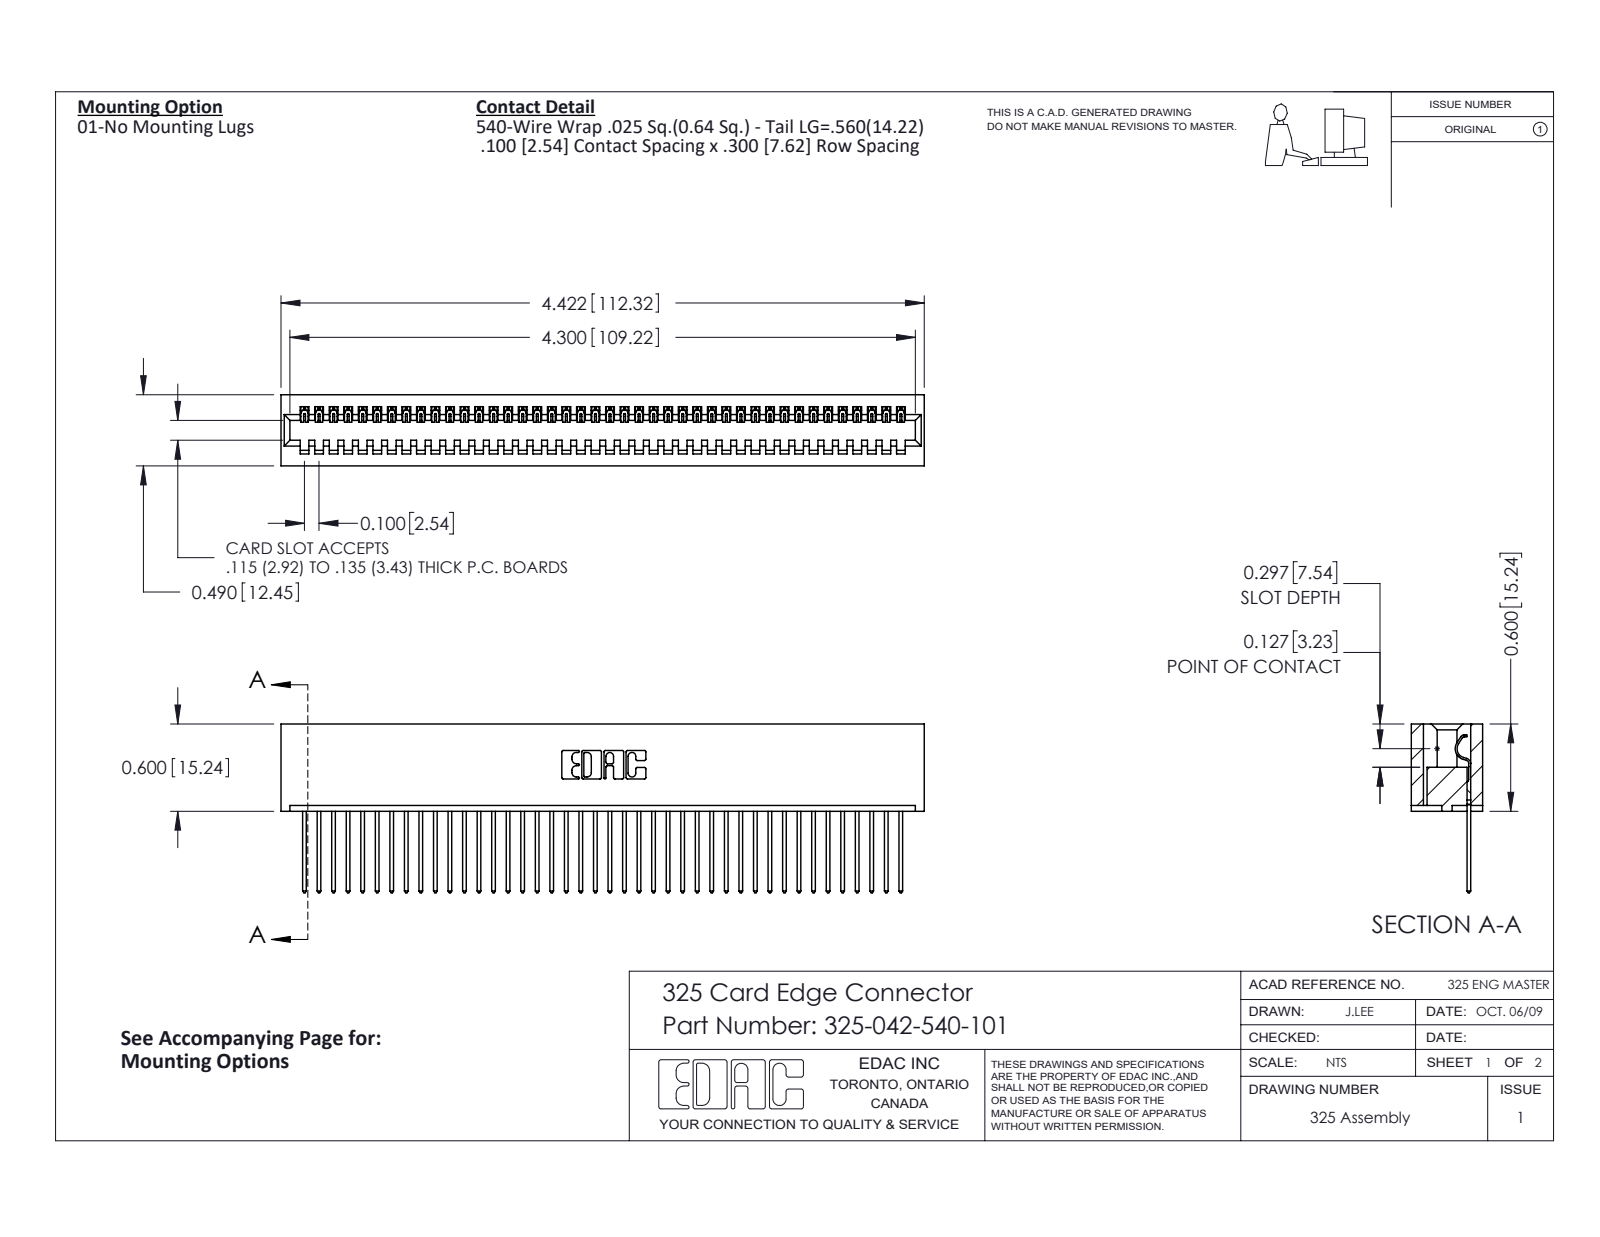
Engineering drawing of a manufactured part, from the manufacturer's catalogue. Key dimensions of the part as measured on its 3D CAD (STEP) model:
Part name (STEP PRODUCT): 325-042-540-101; 325-292-001_325-293-140; 325 Part_Lugless
STEP written by: SolidWorks 2016 (CONFIG_CONTROL_DESIGN)
Units: inches
Bodies: 43 solids, 2542 faces (1830 planar, 712 cylindrical, 0 other)
Overall size (bounding box): 4.422 × 1.16 × 0.49
Volume: 0.908 in³ · Surface area: 26.62 in²
Partial cylindrical surfaces — rounded edges, fillets, slot ends (radius × count): R0.006 ×84, R0.01 ×84, R0.01 ×22, R0.007 ×6, R0.031 ×6, R0.026 ×3, R0.014 ×1, R0.022 ×1
Main face-to-face distances: 0.083, 0.407, 0.49, 0.3, 0.107, 0.383, 0.025, 0.325, 0.56, 0.263
